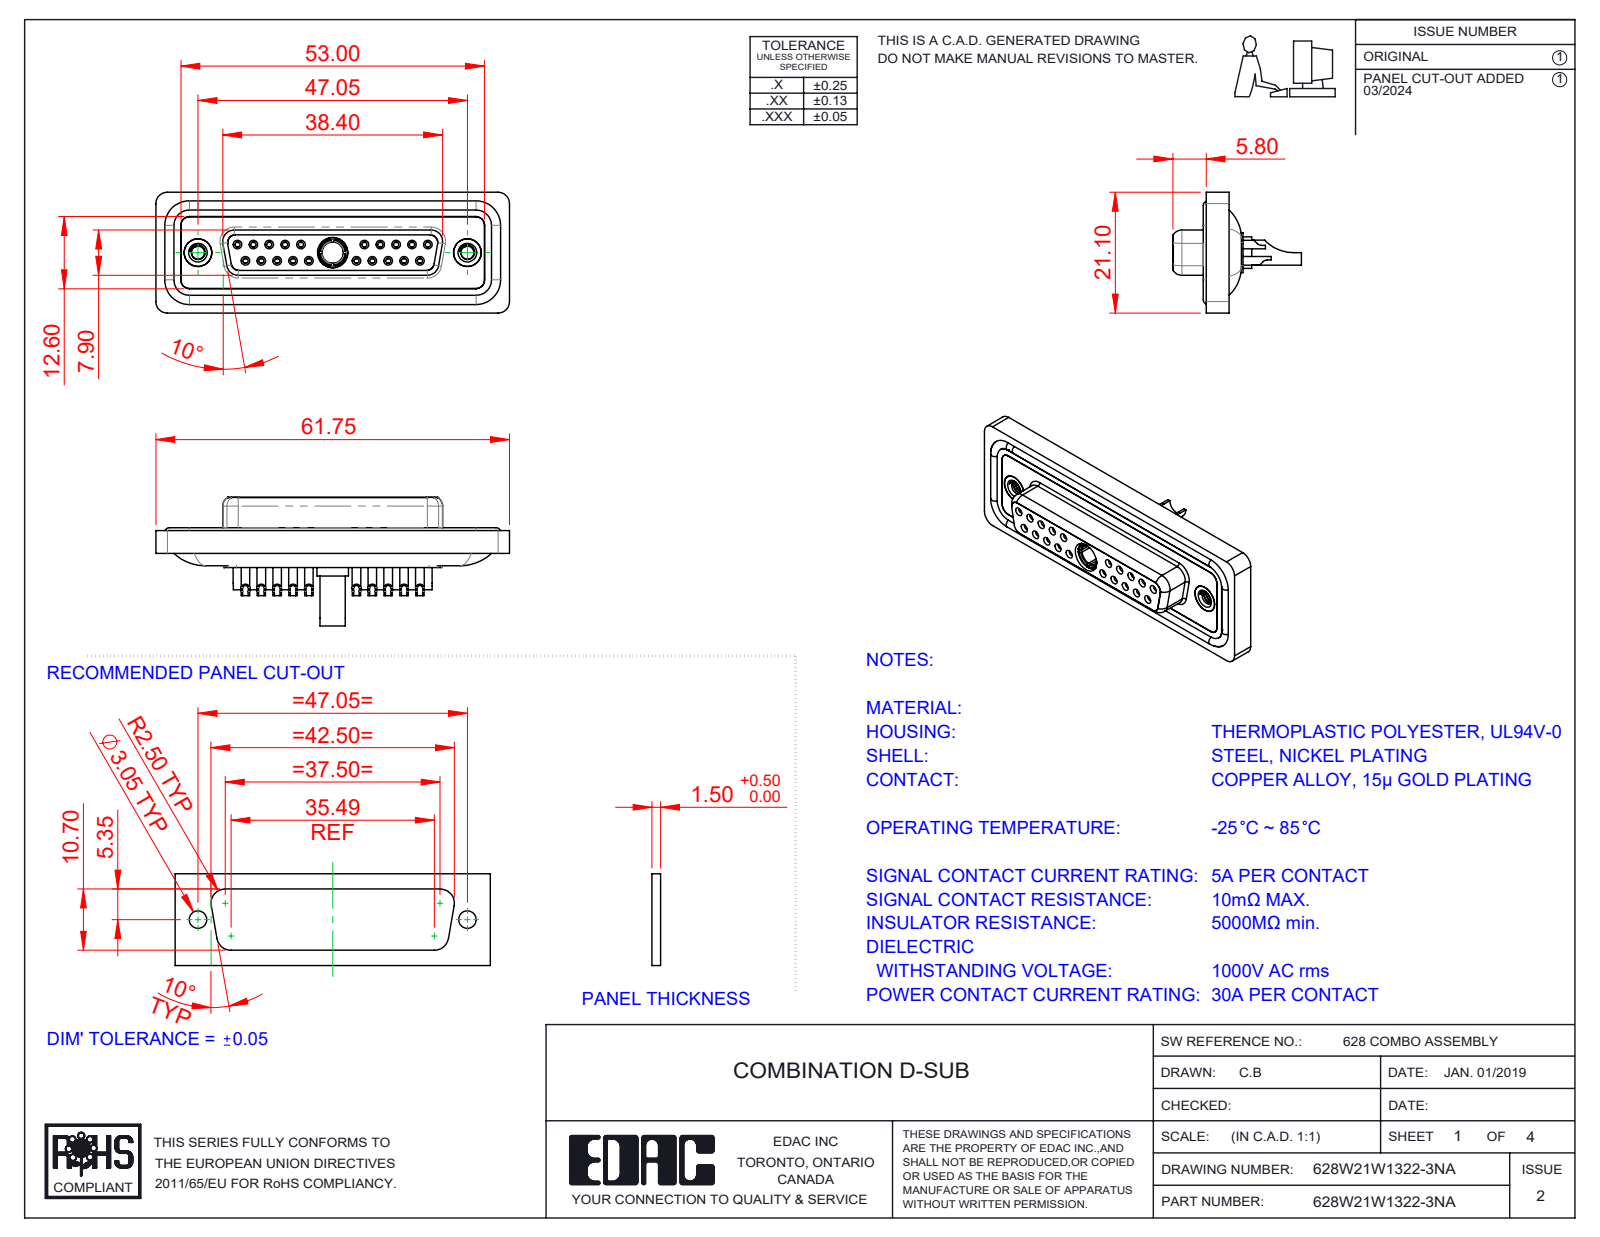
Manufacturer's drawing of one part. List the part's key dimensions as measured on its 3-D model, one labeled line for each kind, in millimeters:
Part name (STEP PRODUCT): 628Combo Shell Front_25 Contacts; 628W21W1322-3NA; 628Combo Contact Row 1_22; 628Combo Contact Row 2_22 (+5 more)
STEP written by: SolidWorks 2023 (CONFIG_CONTROL_DESIGN)
Units: millimetres
Bodies: 29 solids, 1564 faces (477 planar, 636 cylindrical, 451 other)
Overall size (bounding box): 61.75 × 22.45 × 21.1
Volume: 8 440 mm³ · Surface area: 14 317 mm²
Round holes (diameter × count): ⌀0.9 ×20, ⌀1 ×20, ⌀1.1 ×20, ⌀1.5 ×20, ⌀2 ×20, ⌀1.6 ×10, ⌀1.7 ×10, ⌀4.85 ×3, ⌀2.26 ×2, ⌀4 ×2, ⌀4.05 ×2, ⌀5 ×2
Round bosses / shafts (diameter × count): ⌀2.2 ×20, ⌀1.6 ×14, ⌀4.95 ×2, ⌀4.8 ×2, ⌀5.5 ×1, ⌀5.2 ×1, ⌀4.96 ×1, ⌀4.75 ×1
Partial cylindrical surfaces — rounded edges, fillets, slot ends (radius × count): R1.5 ×22, R2 ×18, R1.35 ×8, R1.6 ×8, R1 ×6, R0.25 ×4, R0.5 ×4, R0.6 ×4
Main face-to-face distances: 0.4, 1.8, 7.45, 5.65, 6.6, 0.5, 1.6, 7.05, 2.9, 1.1
Hole centre spacings: 3.16, 2.77, 5.54, 5.03, 8.31, 7.48, 16.62, 19.39
